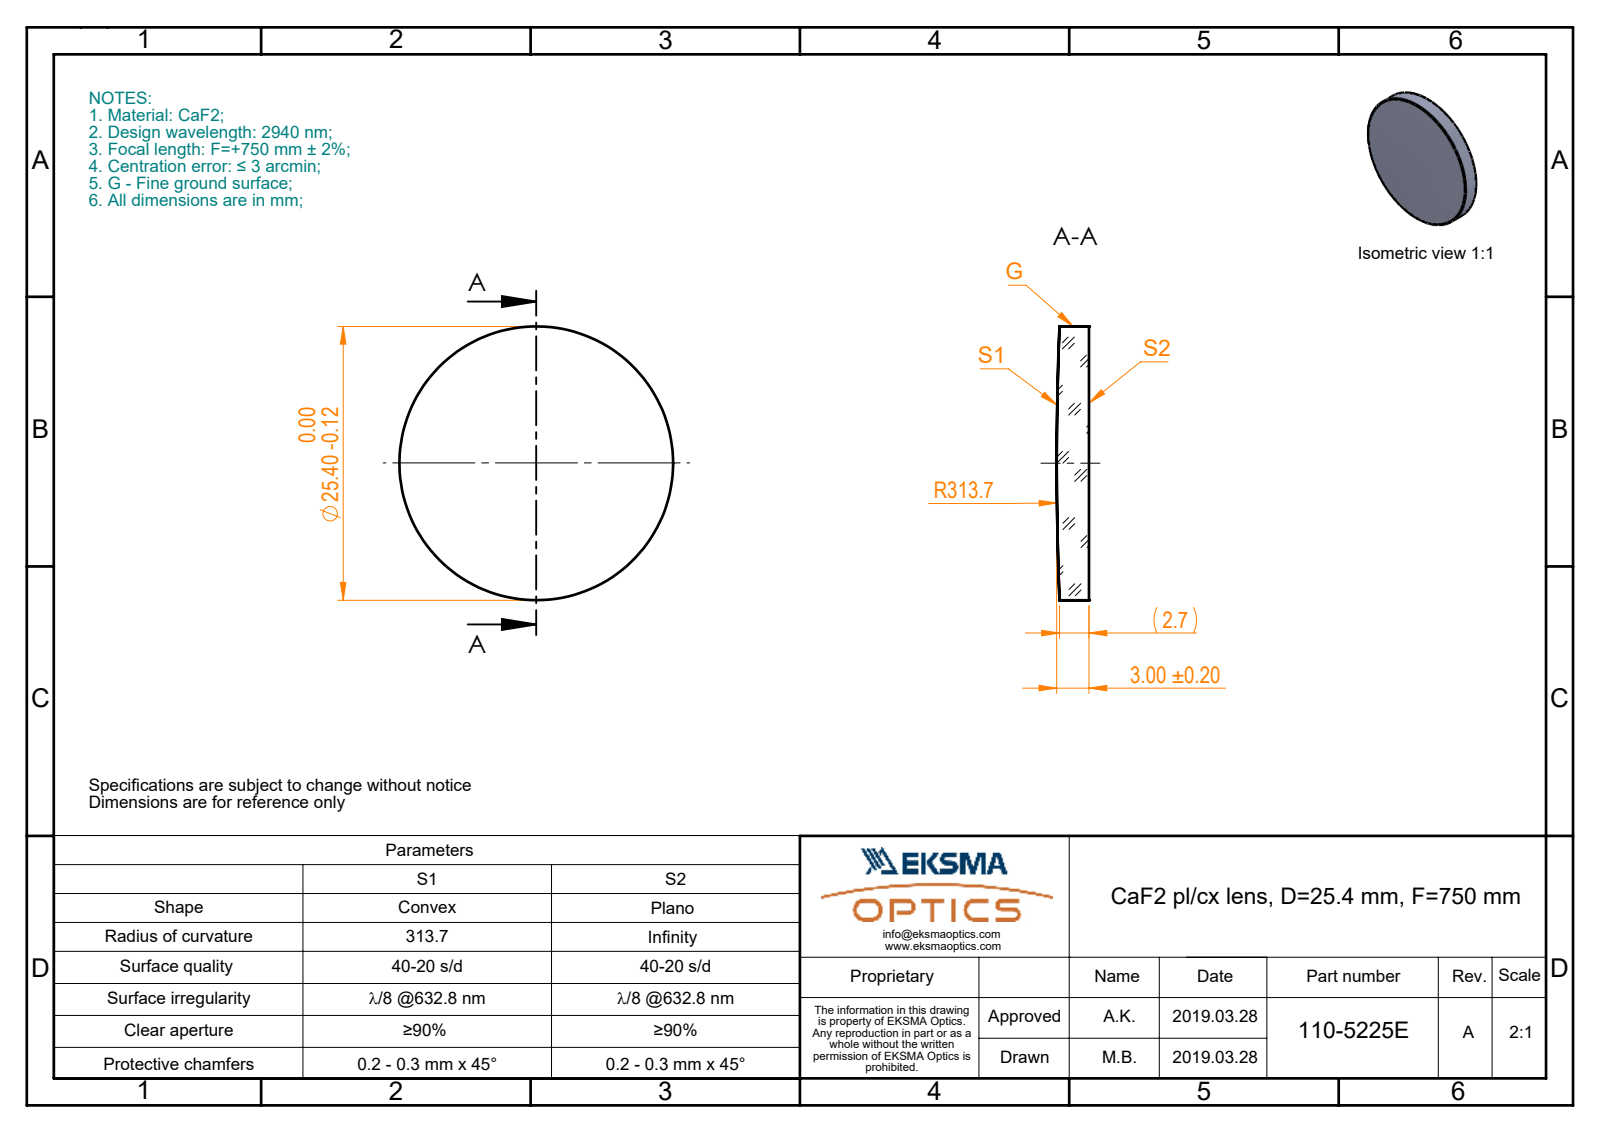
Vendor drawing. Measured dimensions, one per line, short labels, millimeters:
name: 110-5225E CaF2 pl-cx 25.4 F750
written by: SolidWorks 2017 (CONFIG_CONTROL_DESIGN)
unit: mm
bodies: 1 solid, 5 faces (1 planar, 2 cylindrical, 2 other)
size: 25.4 × 25.4 × 3
volume: 1 455 mm³; area: 1 232 mm²
bosses: 1× ⌀25.4
